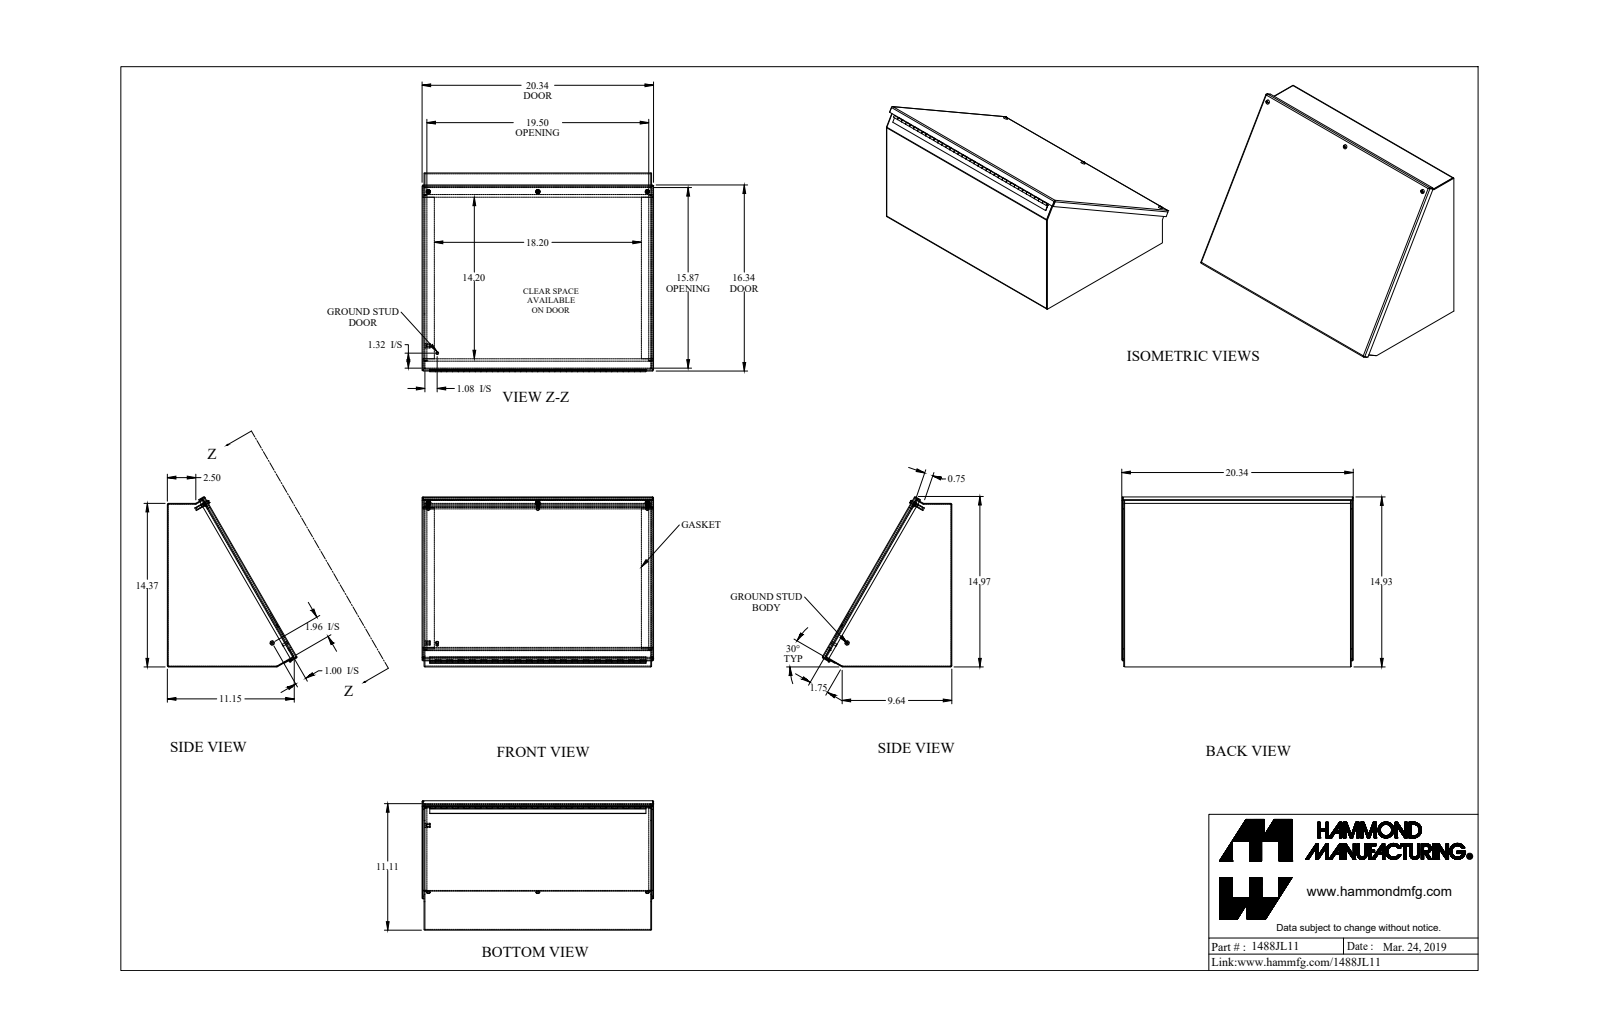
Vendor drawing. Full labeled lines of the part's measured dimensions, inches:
Part name (STEP PRODUCT): 1488JL11_Default
STEP written by: SolidWorks 2019 (CONFIG_CONTROL_DESIGN)
Units: inches
Bodies: 20 solids, 679 faces (452 planar, 195 cylindrical, 32 other)
Overall size (bounding box): 20.343 × 14.933 × 11.374
Volume: 103.4 in³ · Surface area: 2 613 in²
Round holes (diameter × count): ⌀0.159 ×3, ⌀0.25 ×3, ⌀0.156 ×1
Round bosses / shafts (diameter × count): ⌀0.39 ×3, ⌀0.275 ×3, ⌀0.19 ×3, ⌀0.148 ×3, ⌀0.375 ×1, ⌀0.25 ×1, ⌀0.188 ×1, ⌀0.174 ×1
Partial cylindrical surfaces — rounded edges, fillets, slot ends (radius × count): R0.036 ×12, R0.108 ×12, R0.125 ×3, R0.16 ×3, R0.171 ×3
Main face-to-face distances: 0.072, 19.928, 19.856, 20, 14.293, 0.25, 0.322, 14.365, 14.221, 0.197
Hole centre spacings: 9.625, 9.625, 19.25, 19.25
